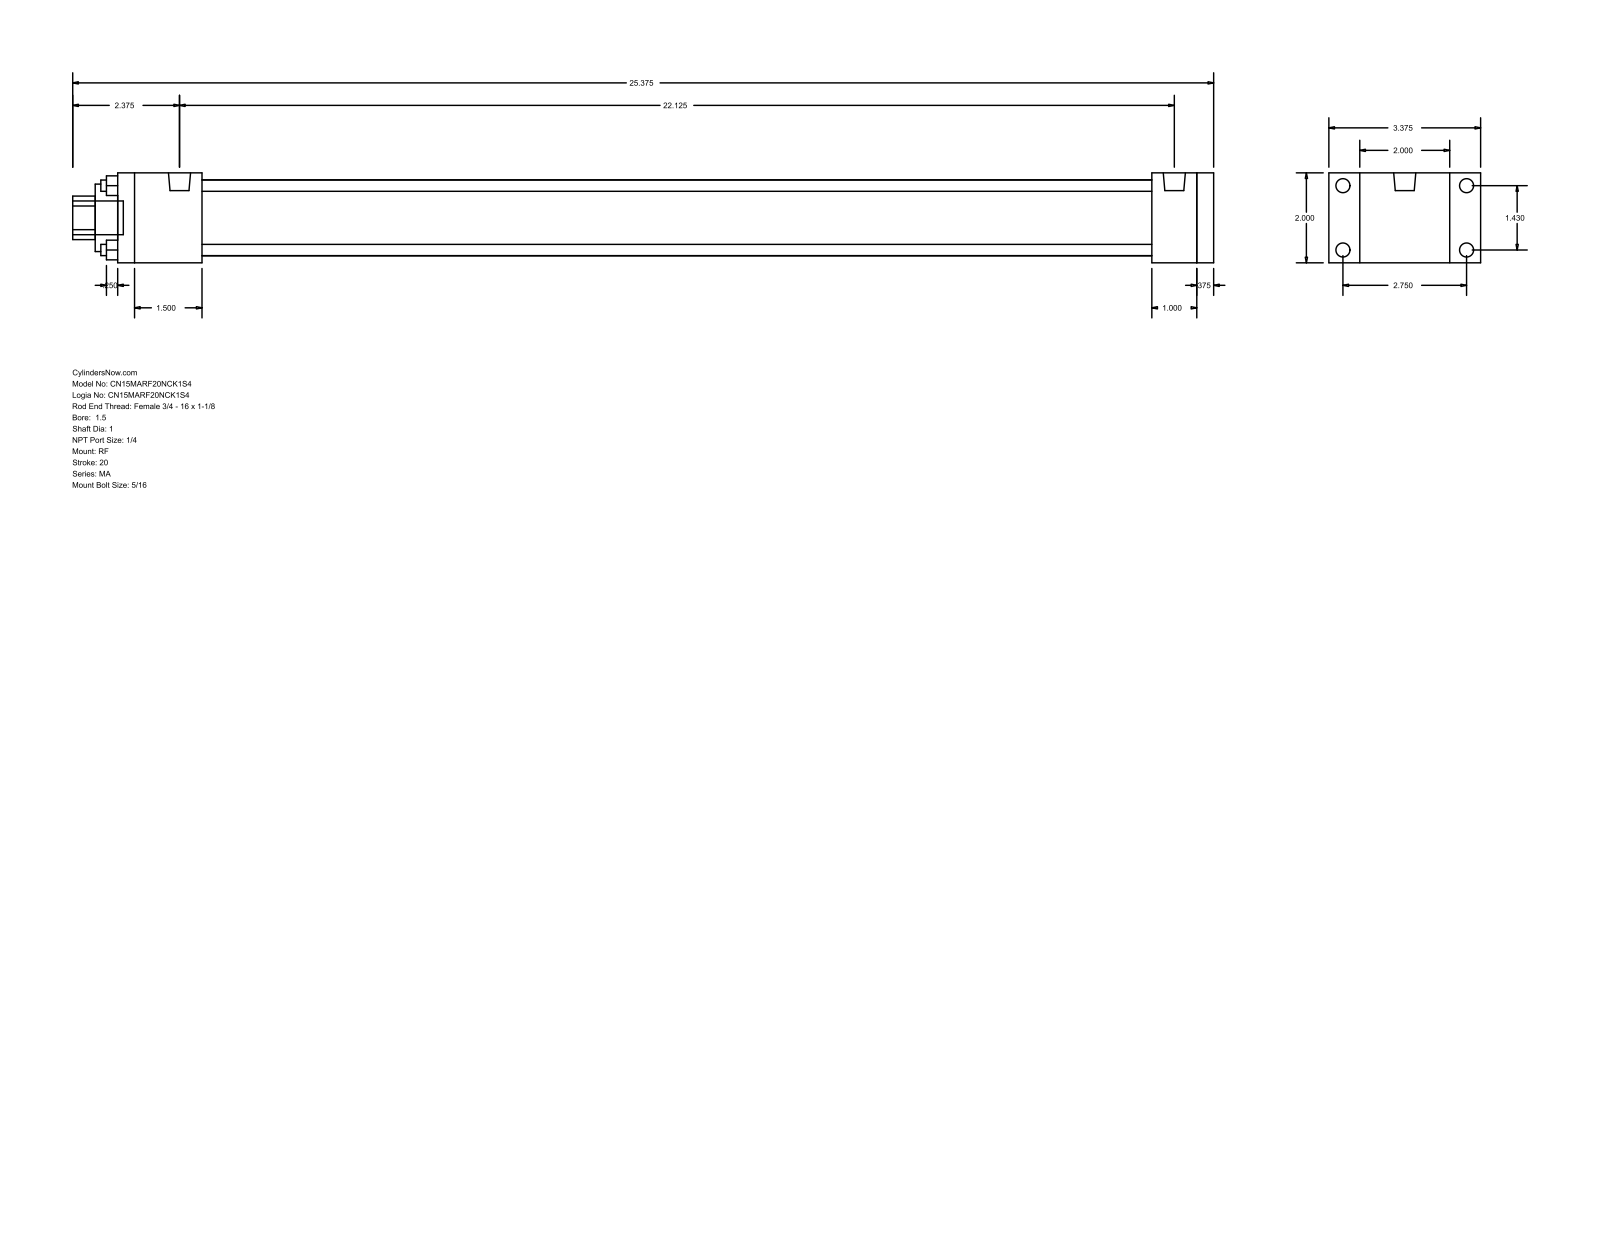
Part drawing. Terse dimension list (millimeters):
name: MA_RF__0150_1
written by: GSSL Pune (CONFIG_CONTROL_DESIGN)
unit: mm
bodies: 0 solids, 92 faces (64 planar, 28 cylindrical, 0 other)
size: 644.52 × 85.72 × 50.8
holes: 4× ⌀6.35, 1× ⌀25.4, 1× ⌀38.1, 1× ⌀42.93
bosses: 8× ⌀7.94, 2× ⌀12.49, 1× ⌀19.05
rounds: 1× R12.29
face distances: 50.8, 9.52, 619.12, 609.6, 25.4, 584.2, 34.92, 47.63, 536.57, 561.97
hole spacings: 25.68, 36.32, 51.36
